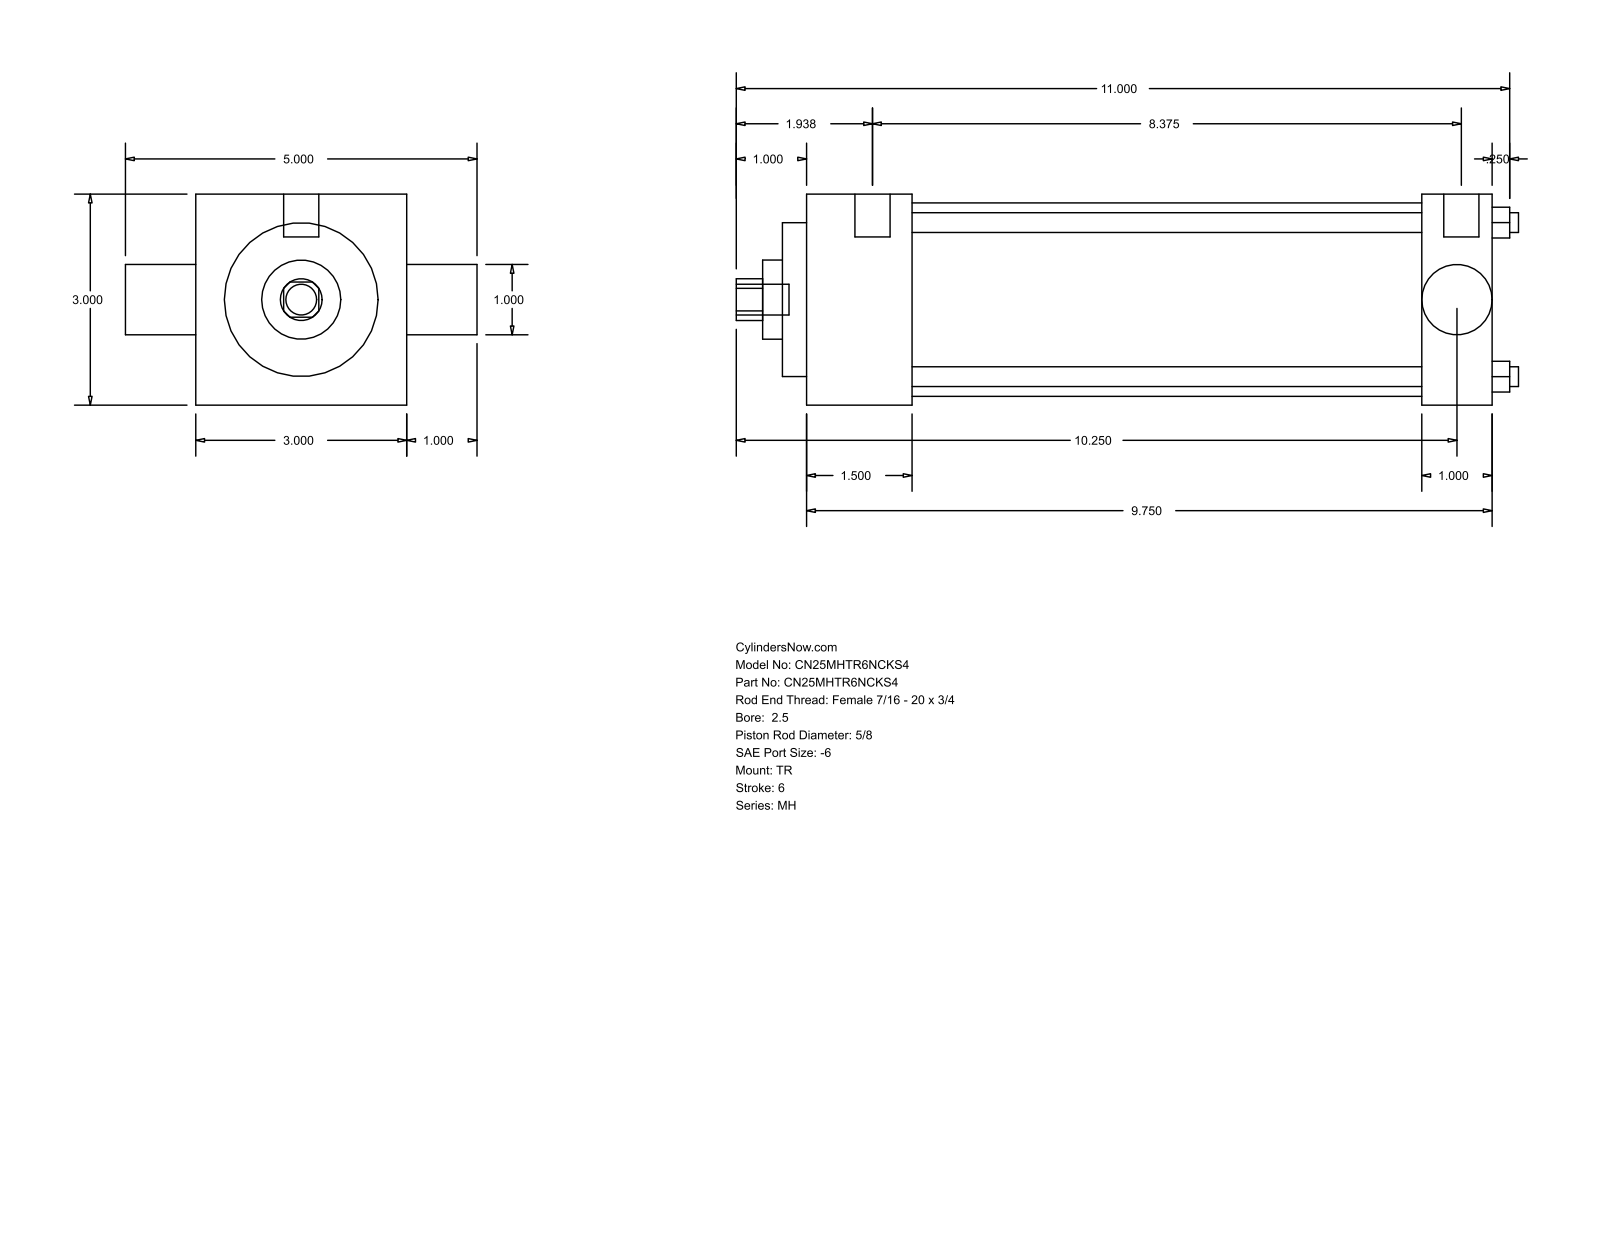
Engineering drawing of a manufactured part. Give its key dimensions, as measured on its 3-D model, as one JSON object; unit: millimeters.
{"part_name": "MH_TR__0250_0.625", "step_written_by": "GSSL Pune (CONFIG_CONTROL_DESIGN)", "units": "millimeters", "bodies": {"solids": 0, "faces": 86, "planar": 61, "cylindrical": 25, "other": 0}, "overall_size": [282.57, 127, 76.2], "round_holes": [[7.14, 4], [15.88, 1], [25.35, 1], [28.57, 1], [55.55, 1], [69.85, 1]], "round_bosses_or_shafts": [[5.56, 3], [12.7, 2], [11.11, 1]], "partial_cylinders_radius": [[7.54, 1]], "face_to_face_distances": [76.2, 247.65, 25.4, 38.1, 209.55, 222.25, 184.15, 8.73, 46.83, 230.98], "hole_center_spacings": [39.33, 55.62, 78.66]}
